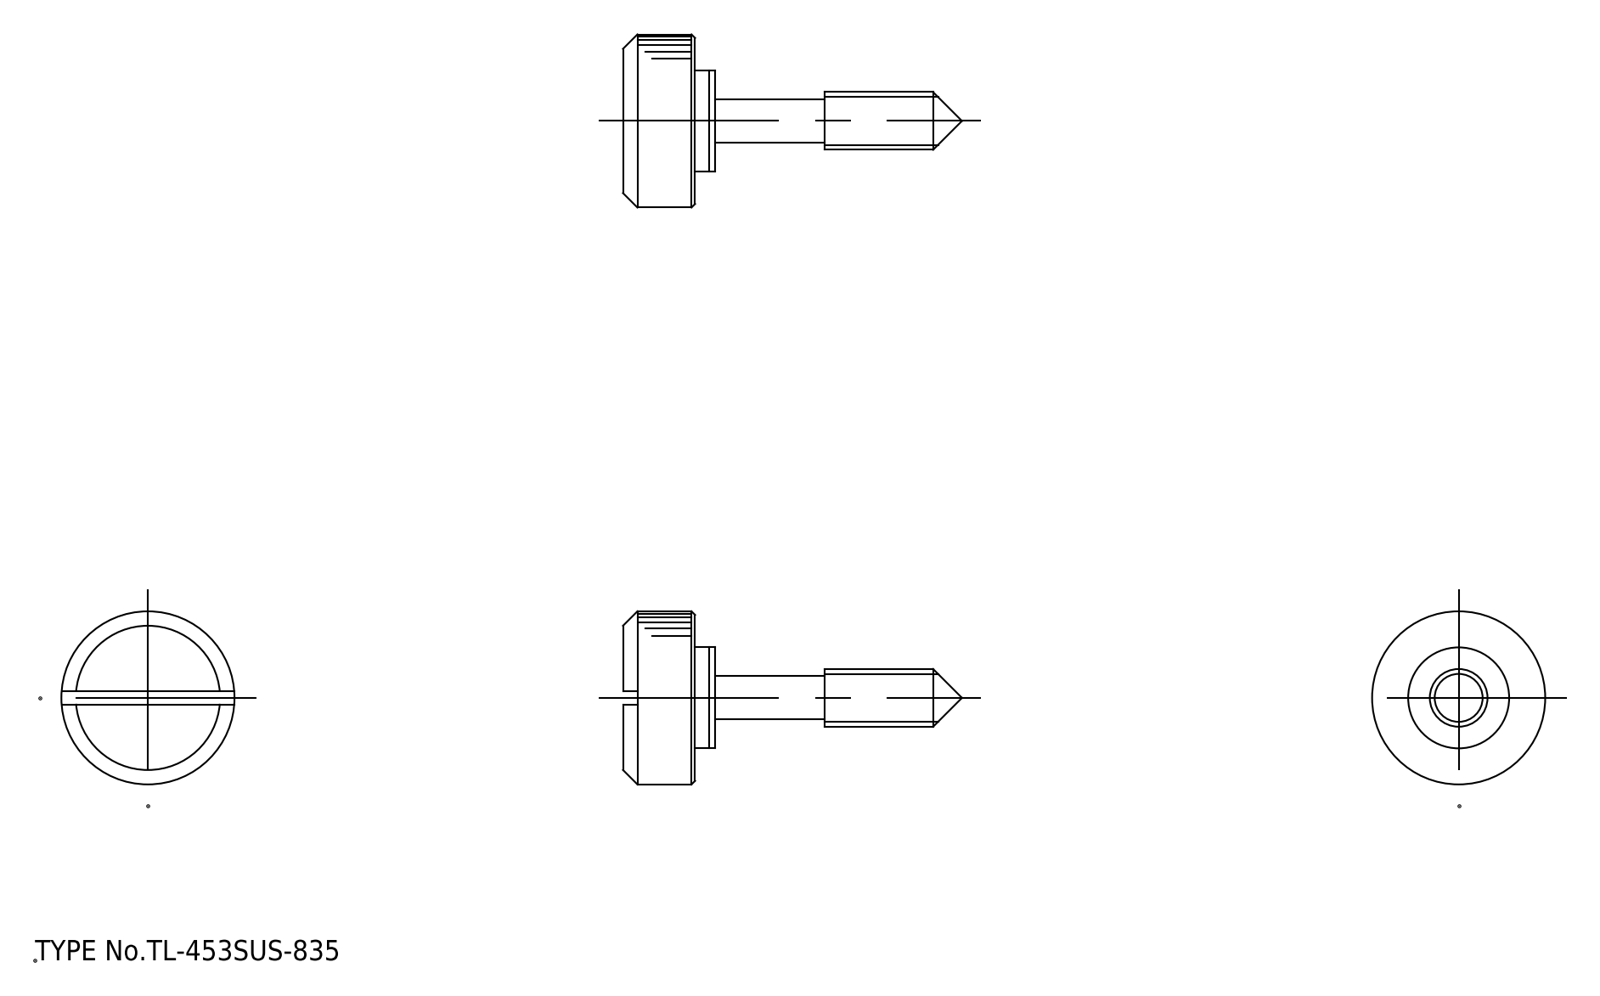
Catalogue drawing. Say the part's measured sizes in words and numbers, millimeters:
The part is named "washer; knob". Its 3-D file was written by "spGate 19.8.4 (****-****-****-****) (AUTOMOTIVE_DESIGN)". It is 2 solids with 42 faces: 18 planar, 18 cylindrical and 6 other. Overall it measures 47 by 24 by 24 millimeters. Its volume is 5 963 cubic millimeters and its surface area 2 734 square millimeters. Round bosses or shafts: 1 of diameter 24, 1 of diameter 14, 1 of diameter 8, 1 of diameter 6. Partial cylindrical surfaces (rounded edges, fillets, slot ends): 4 of radius 1.25, 1 of radius 3.05. The main face-to-face distances are 10, 2, 12, 12.8, 2.8, 0.8, 1.8, 8, 10.8, 28.
